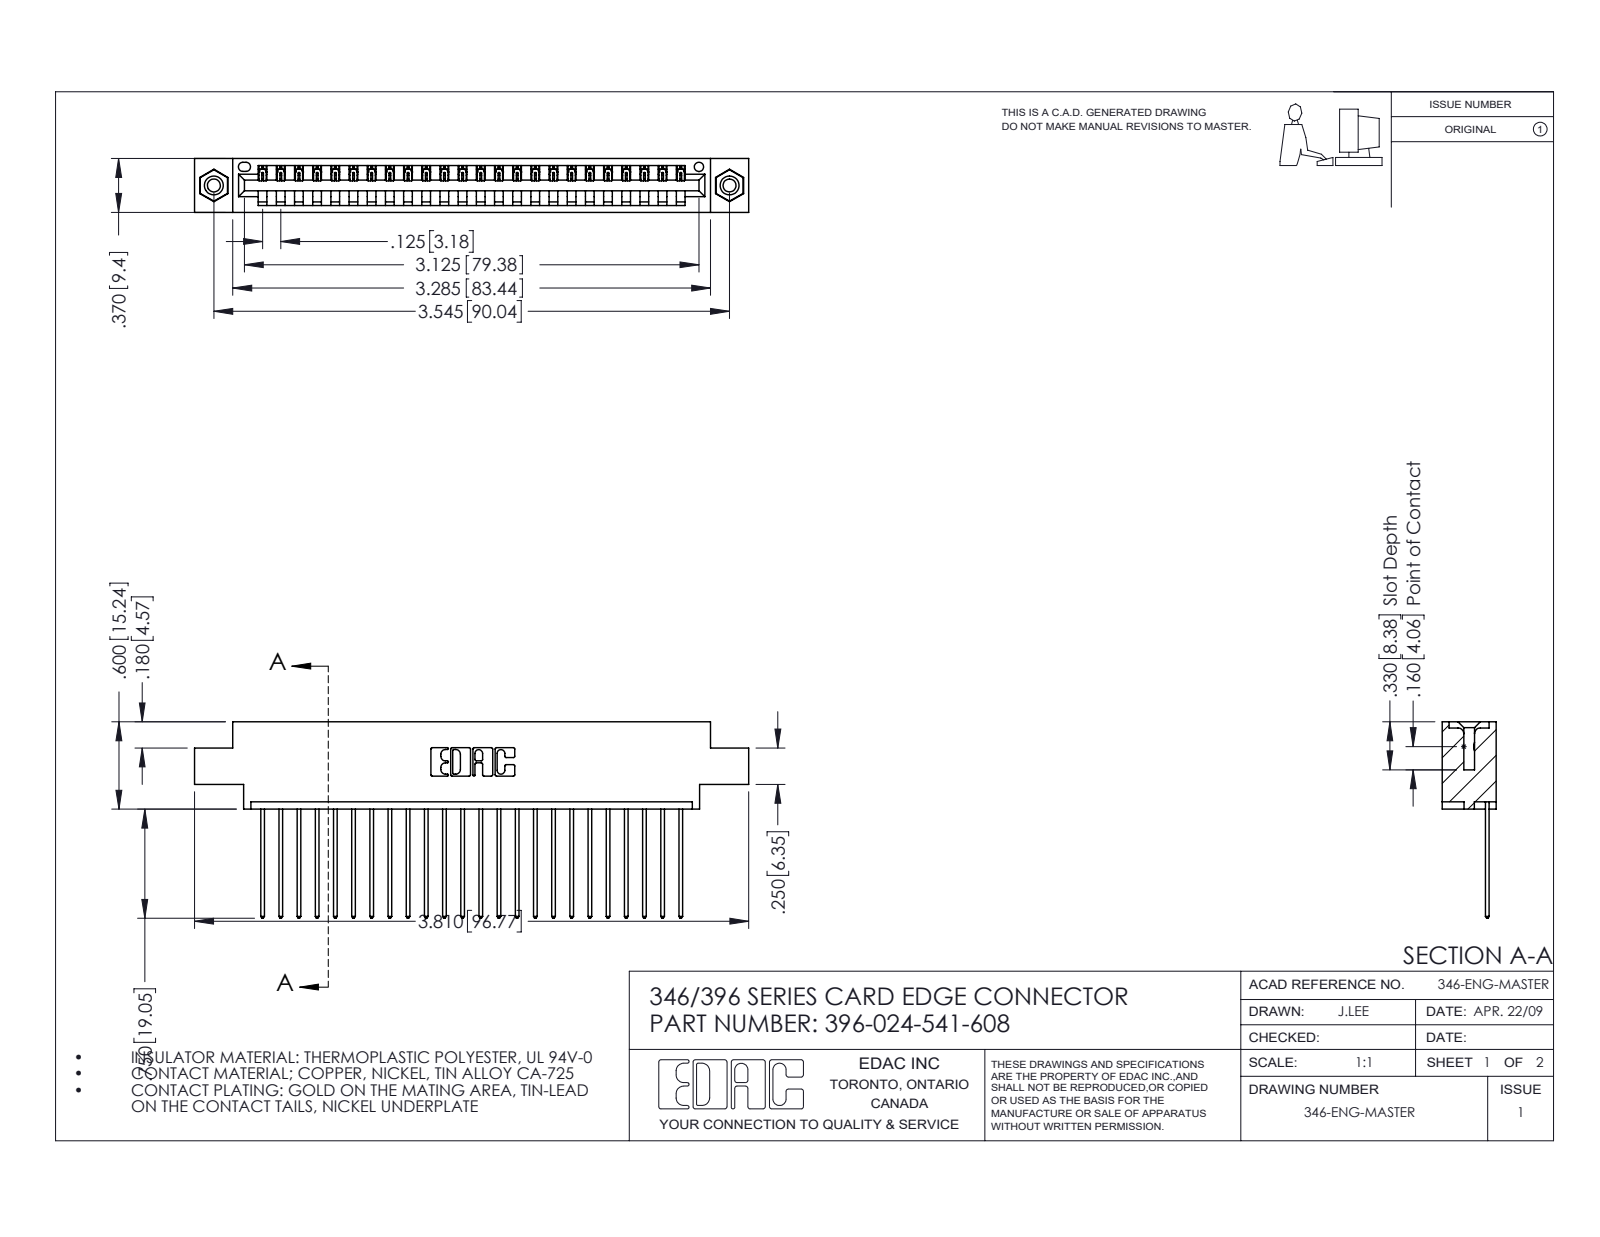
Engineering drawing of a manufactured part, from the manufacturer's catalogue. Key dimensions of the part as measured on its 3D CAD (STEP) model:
Part name (STEP PRODUCT): 396-024-541-608; 346 Part_0.170 Offset - 0.156 Dia-TI; 345-250-001_345-250-003-102; 345-292-001_345-293-141
STEP written by: SolidWorks 2016 (CONFIG_CONTROL_DESIGN)
Units: inches
Bodies: 27 solids, 1578 faces (1072 planar, 490 cylindrical, 16 other)
Overall size (bounding box): 3.81 × 1.35 × 0.37
Volume: 0.553 in³ · Surface area: 18.26 in²
Round holes (diameter × count): ⌀0.089 ×2, ⌀0.125 ×2, ⌀0.156 ×2, ⌀0.064 ×1
Round bosses / shafts (diameter × count): ⌀0.155 ×2
Partial cylindrical surfaces — rounded edges, fillets, slot ends (radius × count): R0.006 ×48, R0.01 ×48, R0.01 ×22, R0.007 ×6, R0.031 ×6, R0.026 ×3, R0.031 ×2, R0.04 ×2
Main face-to-face distances: 0.048, 0.322, 0.37, 0.25, 0.072, 0.298, 0.025, 0.222, 0.148, 0.1
Hole centre spacings: 0.246, 3.337, 3.545
